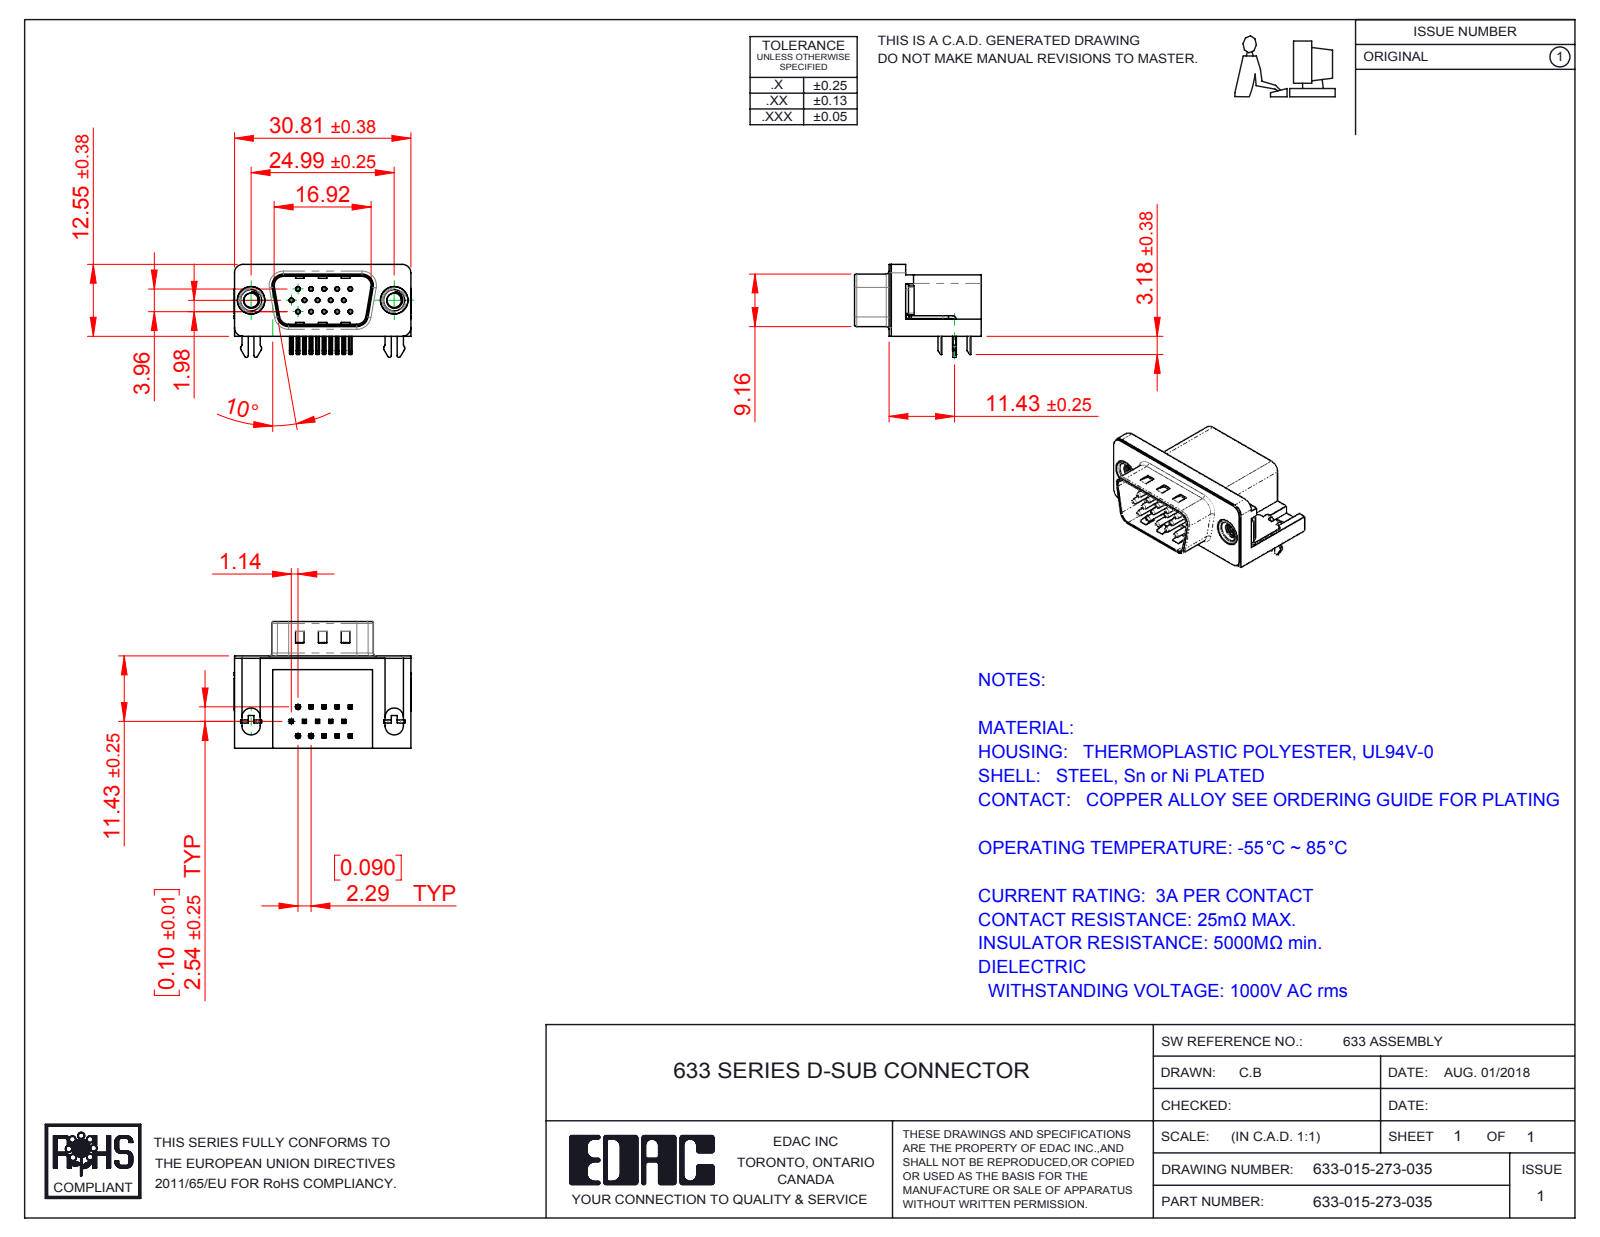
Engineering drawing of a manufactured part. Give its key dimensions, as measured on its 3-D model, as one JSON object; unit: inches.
{"part_name": "633 M3 Threaded Rivet; 633-015-273-035; 633 2 Prong Board Lock; 633 Contact Top (+5 more)", "step_written_by": "SolidWorks 2016 (CONFIG_CONTROL_DESIGN)", "units": "inches", "bodies": {"solids": 21, "faces": 1483, "planar": 893, "cylindrical": 455, "other": 135}, "overall_size": [1.216, 0.87, 0.64], "volume_in3": 0.248, "surface_area_in2": 8.415, "round_holes": [[0.014, 15], [0.031, 15], [0.098, 2], [0.157, 2], [0.189, 2], [0.197, 2]], "round_bosses_or_shafts": [[0.03, 15], [0.193, 2], [0.187, 2], [0.154, 2]], "partial_cylinders_radius": [[0.01, 68], [0.005, 30], [0.039, 16], [0.02, 14], [0.063, 8], [0.059, 7], [0.013, 4], [0.035, 4]], "face_to_face_distances": [0.016, 0.407, 0.618, 0.114, 0.02, 0.264, 0.634, 0.098, 0.014, 0.421], "hole_center_spacings": [0.156, 0.09, 0.18, 0.09, 0.238, 0.27, 0.312, 0.238]}
